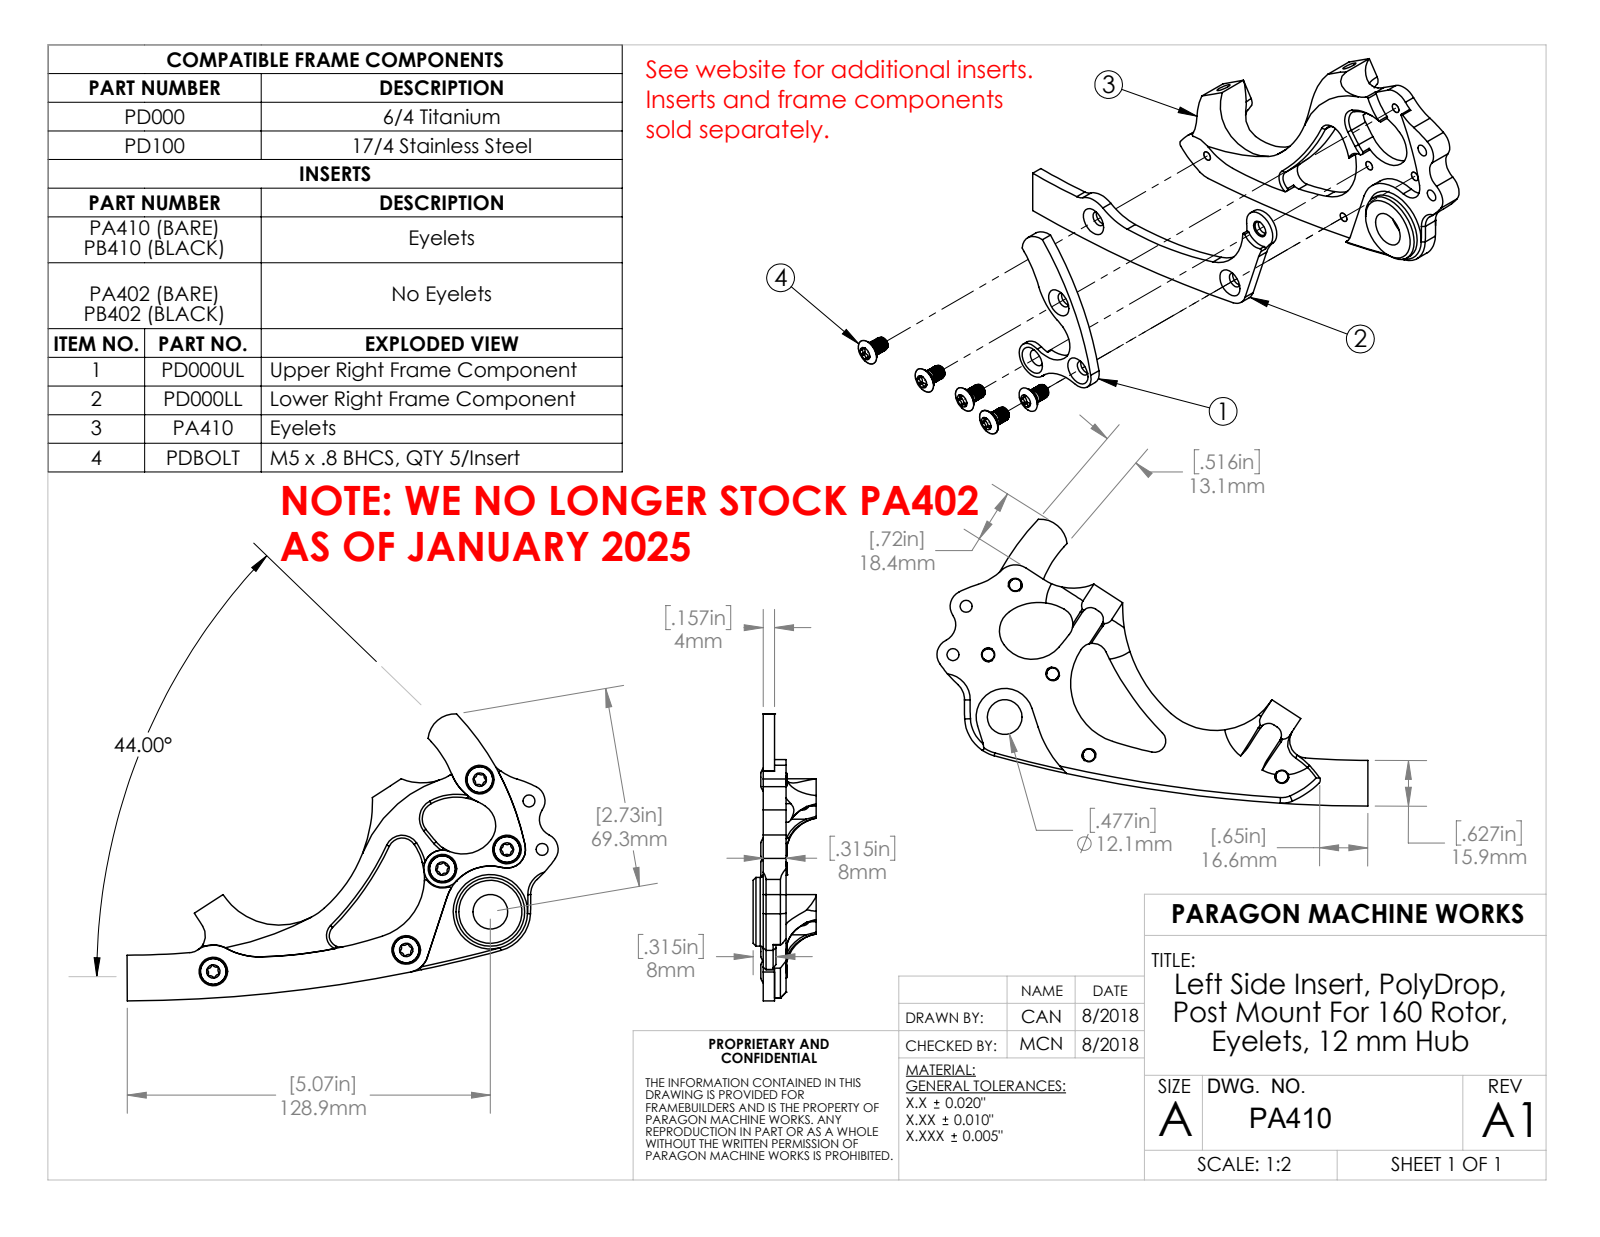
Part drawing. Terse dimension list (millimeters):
name: PA410
written by: SolidWorks 2016 (AUTOMOTIVE_DESIGN)
unit: mm
bodies: 1 solid, 162 faces (23 planar, 93 cylindrical, 46 other)
size: 133.88 × 83.25 × 22
volume: 28 895 mm³; area: 14 847 mm²
holes: 5× ⌀3.3, 2× ⌀4.2, 2× ⌀5, 1× ⌀12.12
bosses: 1× ⌀24
rounds: 9× R0.5, 4× R3.3, 4× R12.7, 3× R6, 3× R7, 2× R5.59, 2× R6.5, 2× R30.71
face distances: 4, 8, 3.5, 4.5, 0.5, 7.5, 11.5, 22, 18.5, 14.5
hole spacings: 22.5, 12.3, 17.5, 18.6, 18.73, 23.48, 26.16, 28.31
